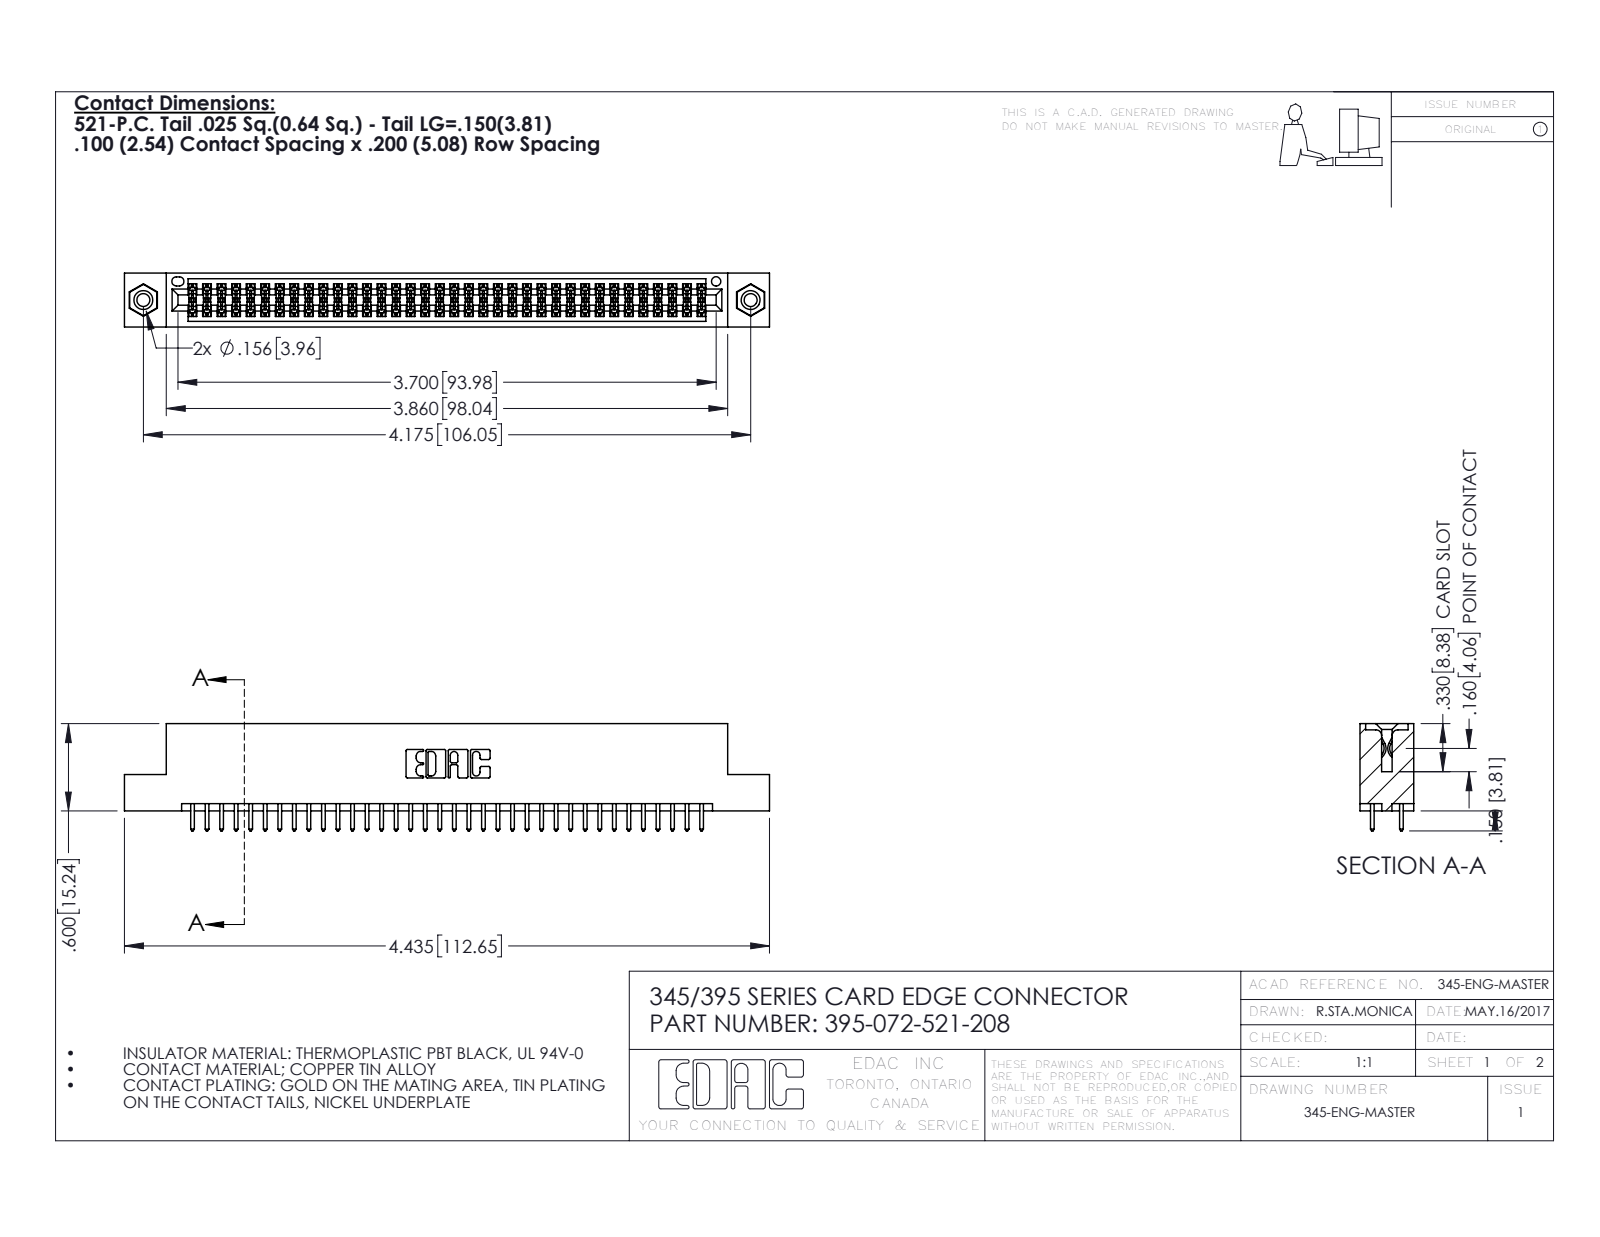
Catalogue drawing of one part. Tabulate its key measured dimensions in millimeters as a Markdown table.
| quantity | value |
| --- | --- |
| part name | 345 Part_Flush Mounting Lugs - 0.156 Dia-TI; 345-250-001_345-250-003-102; 395-072-521-208; 345-292-001_345-293-121 |
| STEP written by | SolidWorks 2016 (CONFIG_CONTROL_DESIGN) |
| units | millimeters |
| bodies | 75 solids, 3786 faces (2488 planar, 1282 cylindrical, 16 other) |
| overall size | 112.6 × 18.7 × 9.4 |
| volume | 10 800 mm³ |
| surface area | 15 750 mm² |
| round holes (diameter × count) | 2.3 × 2, 3.2 × 2, 4 × 2, 1.6 × 1 |
| round bosses / shafts (diameter × count) | 3.9 × 2 |
| partial cylindrical surfaces (radius × count) | 0.2 × 108, 0.3 × 72, 0.3 × 22, 0.2 × 6, 0.8 × 6, 0.7 × 3, 0.4 × 2, 0.5 × 2 |
| main face-to-face distances | 1.8, 7.6, 5.1, 9.4, 2.5, 6.9, 0.6, 5.7, 4.4, 3.8 |
| hole center spacings | 6.9, 100.1, 106 |
